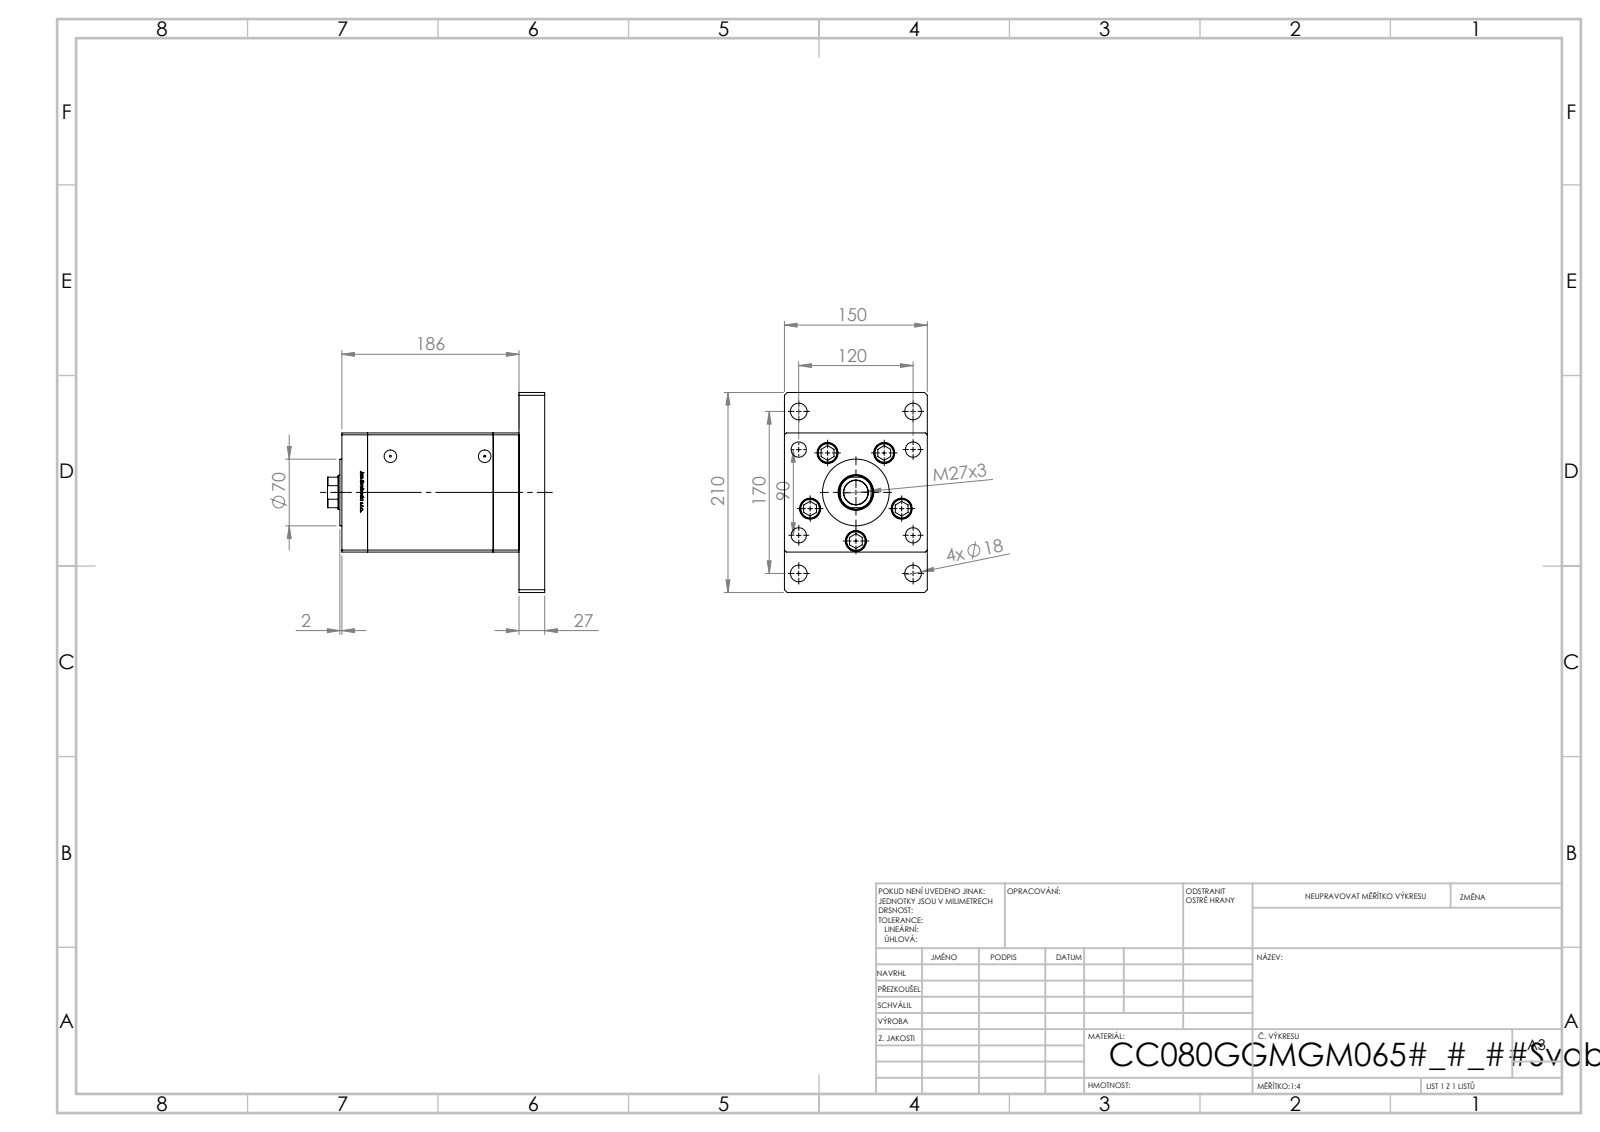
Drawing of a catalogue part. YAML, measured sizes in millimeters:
part_name: "V220C_VC_G; V220C BACK_G; V220C_F; V220C_FRONT_G (+2 more)"
step_written_by: "SolidWorks 2019 (CONFIG_CONTROL_DESIGN)"
units: millimeters
bodies: {solids: 19, faces: 1313, planar: 518, cylindrical: 189, other: 606}
overall_size: [228, 210, 150]
volume: 3827000
surface_area: 435324
round_holes:
  - {diameter: 16, count: 9}
  - {diameter: 17.5, count: 9}
  - {diameter: 22, count: 5}
  - {diameter: 21, count: 4}
  - {diameter: 2, count: 2}
  - {diameter: 13.16, count: 2}
  - {diameter: 25.5, count: 1}
  - {diameter: 36, count: 1}
  - {diameter: 37.5, count: 1}
  - {diameter: 102, count: 1}
round_bosses_or_shafts:
  - {diameter: 8, count: 9}
  - {diameter: 21, count: 5}
  - {diameter: 80, count: 1}
  - {diameter: 70, count: 1}
partial_cylinders:
  - {radius: 0.93, count: 2}
  - {radius: 17.5, count: 1}
face_to_face_distances: [27, 159, 186, 150, 132, 54, 125, 2, 213, 184]
hole_center_spacings: [51, 40, 75, 104.04, 120, 126.49, 130, 176.92]
